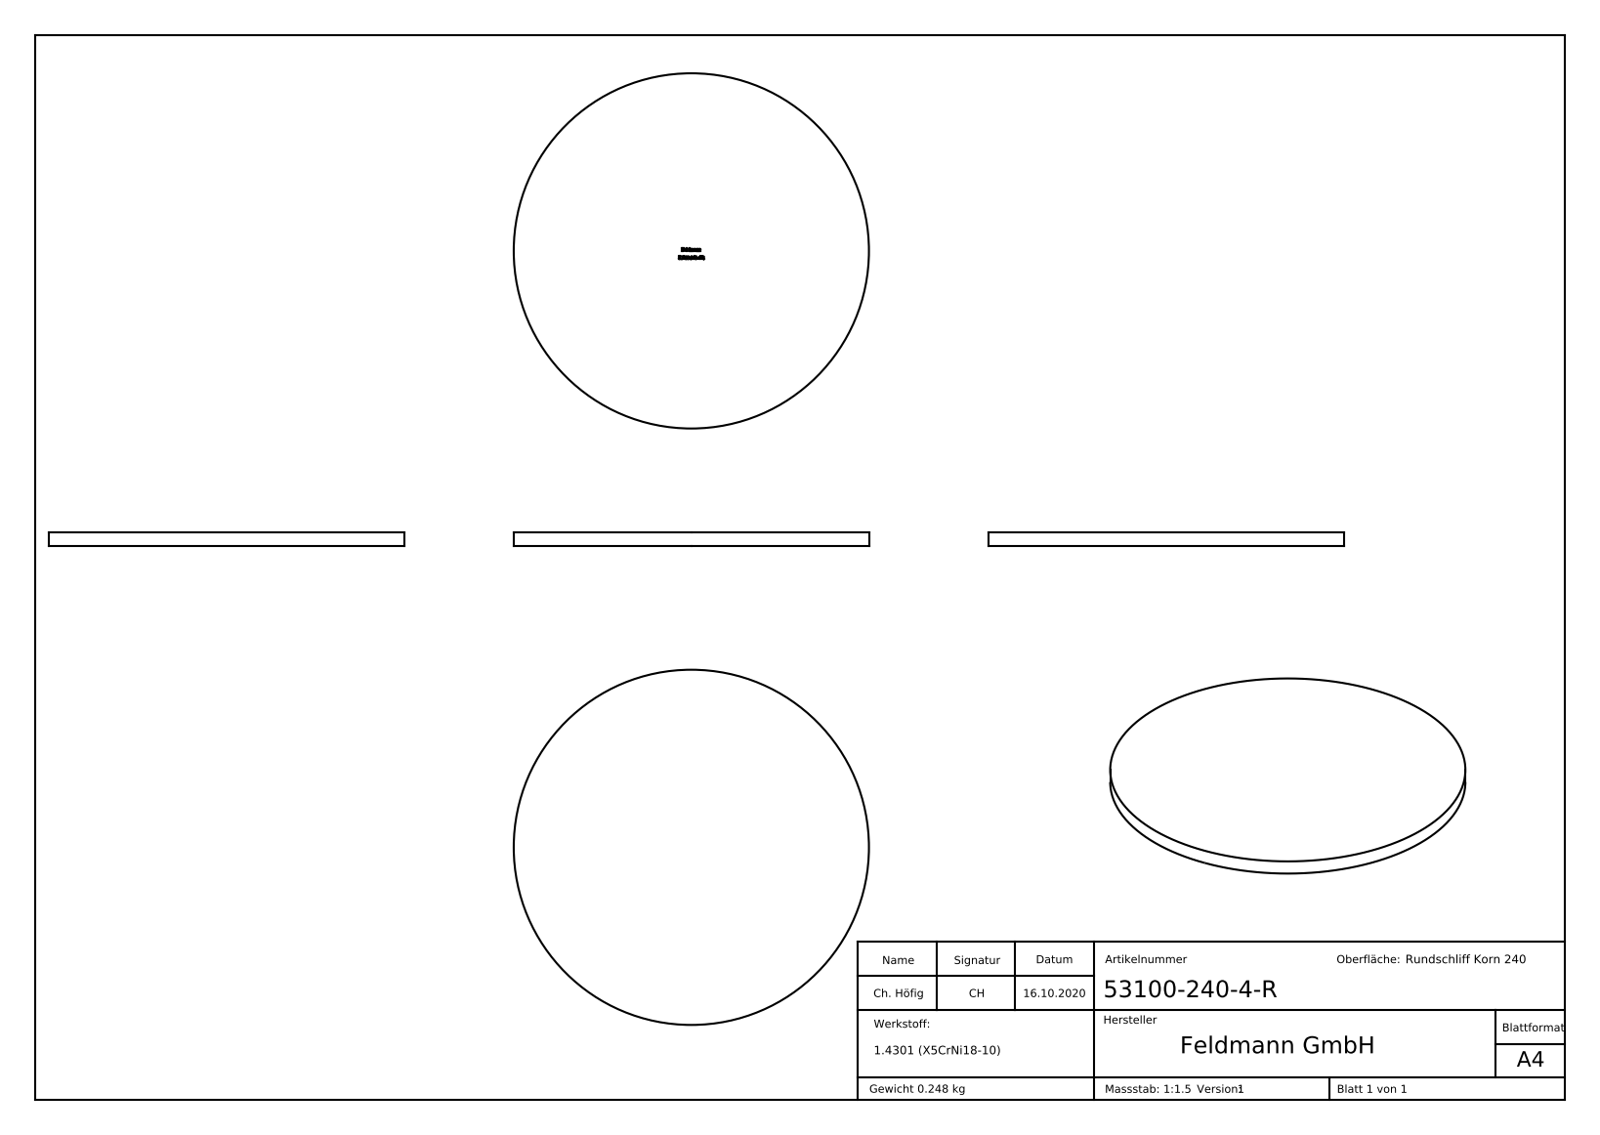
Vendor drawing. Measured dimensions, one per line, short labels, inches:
name: 53100-240-4-R
written by: SolidWorks 2018 (CONFIG_CONTROL_DESIGN)
unit: in
bodies: 1 solid, 266 faces (156 planar, 2 cylindrical, 108 other)
size: 3.937 × 3.937 × 0.157
volume: 1.917 in³; area: 26.31 in²
bosses: 1× ⌀3.937
face distances: 0.157, 0.154, 0.028, 0.048, 0.148, 0.021, 0.026, 0.033, 0.018, 0.074
